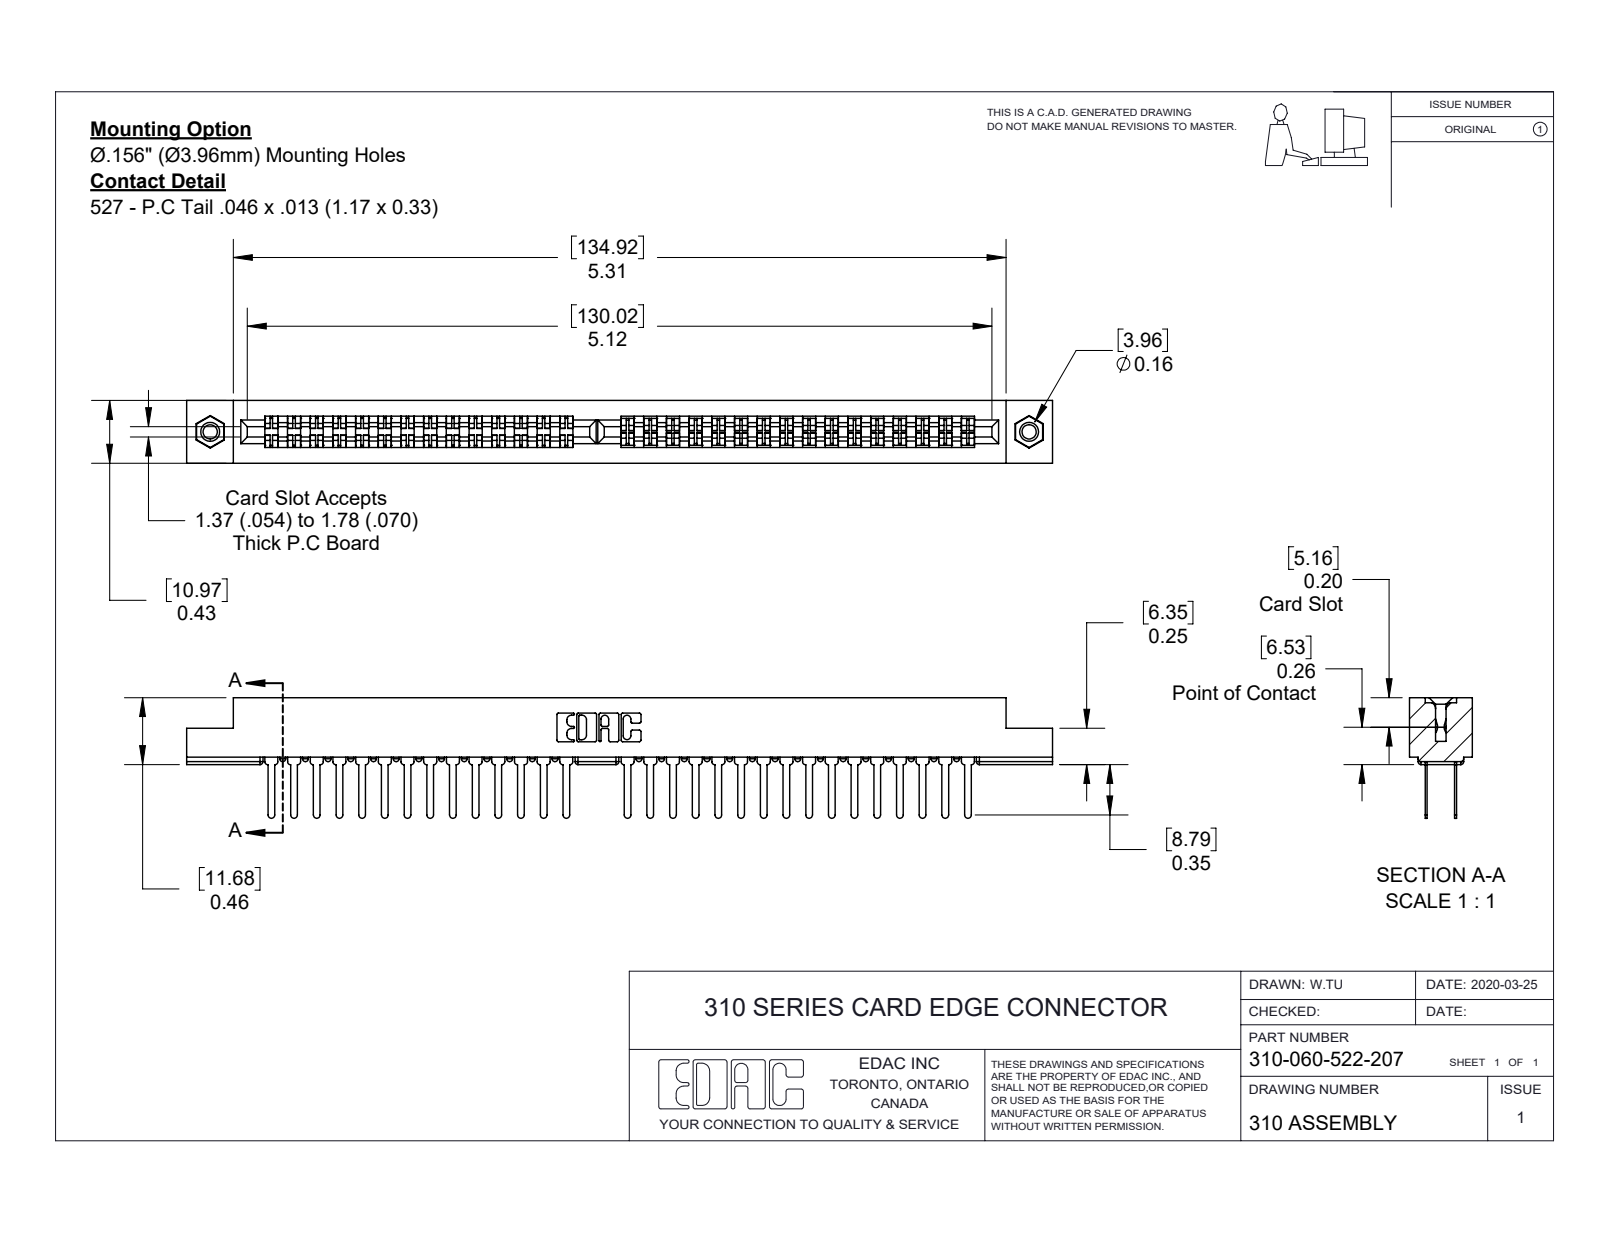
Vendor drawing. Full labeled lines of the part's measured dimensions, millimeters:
Part name (STEP PRODUCT): 345-250-001_345-250-005-103; 310 Part_.116 Hex; 310-060-522-207; 307-290-001_522
STEP written by: SolidWorks 2016 (CONFIG_CONTROL_DESIGN)
Units: millimetres
Bodies: 63 solids, 2986 faces (1976 planar, 930 cylindrical, 80 other)
Overall size (bounding box): 151.21 × 21.06 × 10.97
Volume: 13 126 mm³ · Surface area: 18 608 mm²
Round holes (diameter × count): ⌀2.5 ×2, ⌀3.17 ×2, ⌀3.96 ×2
Round bosses / shafts (diameter × count): ⌀3.94 ×2
Partial cylindrical surfaces — rounded edges, fillets, slot ends (radius × count): R0.51 ×158, R0.58 ×30, R0.25 ×22, R0.17 ×6, R0.8 ×6, R0.3 ×4, R0.64 ×4, R1.19 ×4
Main face-to-face distances: 2.76, 8.22, 0.33, 0.38, 4.75, 10.98, 5.08, 3.14, 7.84, 5.46
Hole centre spacings: 143
